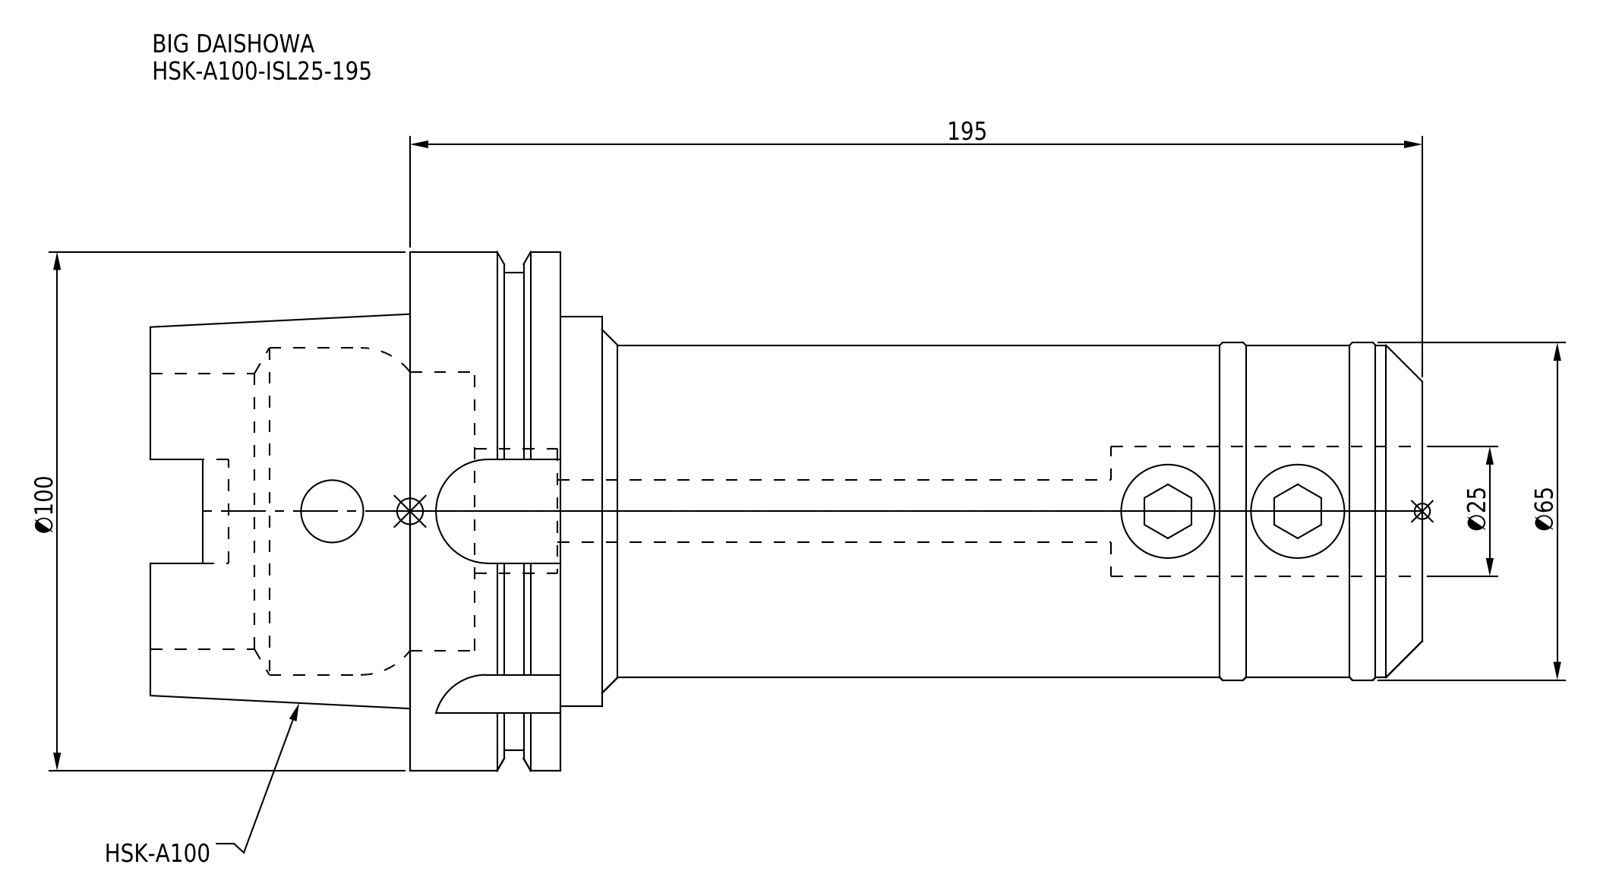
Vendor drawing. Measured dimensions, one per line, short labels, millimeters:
name: HSK-A100-ISL25-195
written by: CREO PARAMETRIC BY PTC INC, 2016380 (AUTOMOTIVE_DESIGN)
unit: mm
bodies: 1 solid, 96 faces (30 planar, 42 cylindrical, 24 other)
size: 245 × 100 × 100
volume: 753 607 mm³; area: 91 463 mm²
holes: 2× ⌀12, 1× ⌀24, 1× ⌀25, 1× ⌀53, 1× ⌀53.8, 1× ⌀63
bosses: 1× ⌀100, 1× ⌀92, 1× ⌀75, 1× ⌀65, 1× ⌀64
rounds: 4× R10
face distances: 29, 16.55, 12.45, 166, 182.55, 195, 245, 79, 62.45, 50
